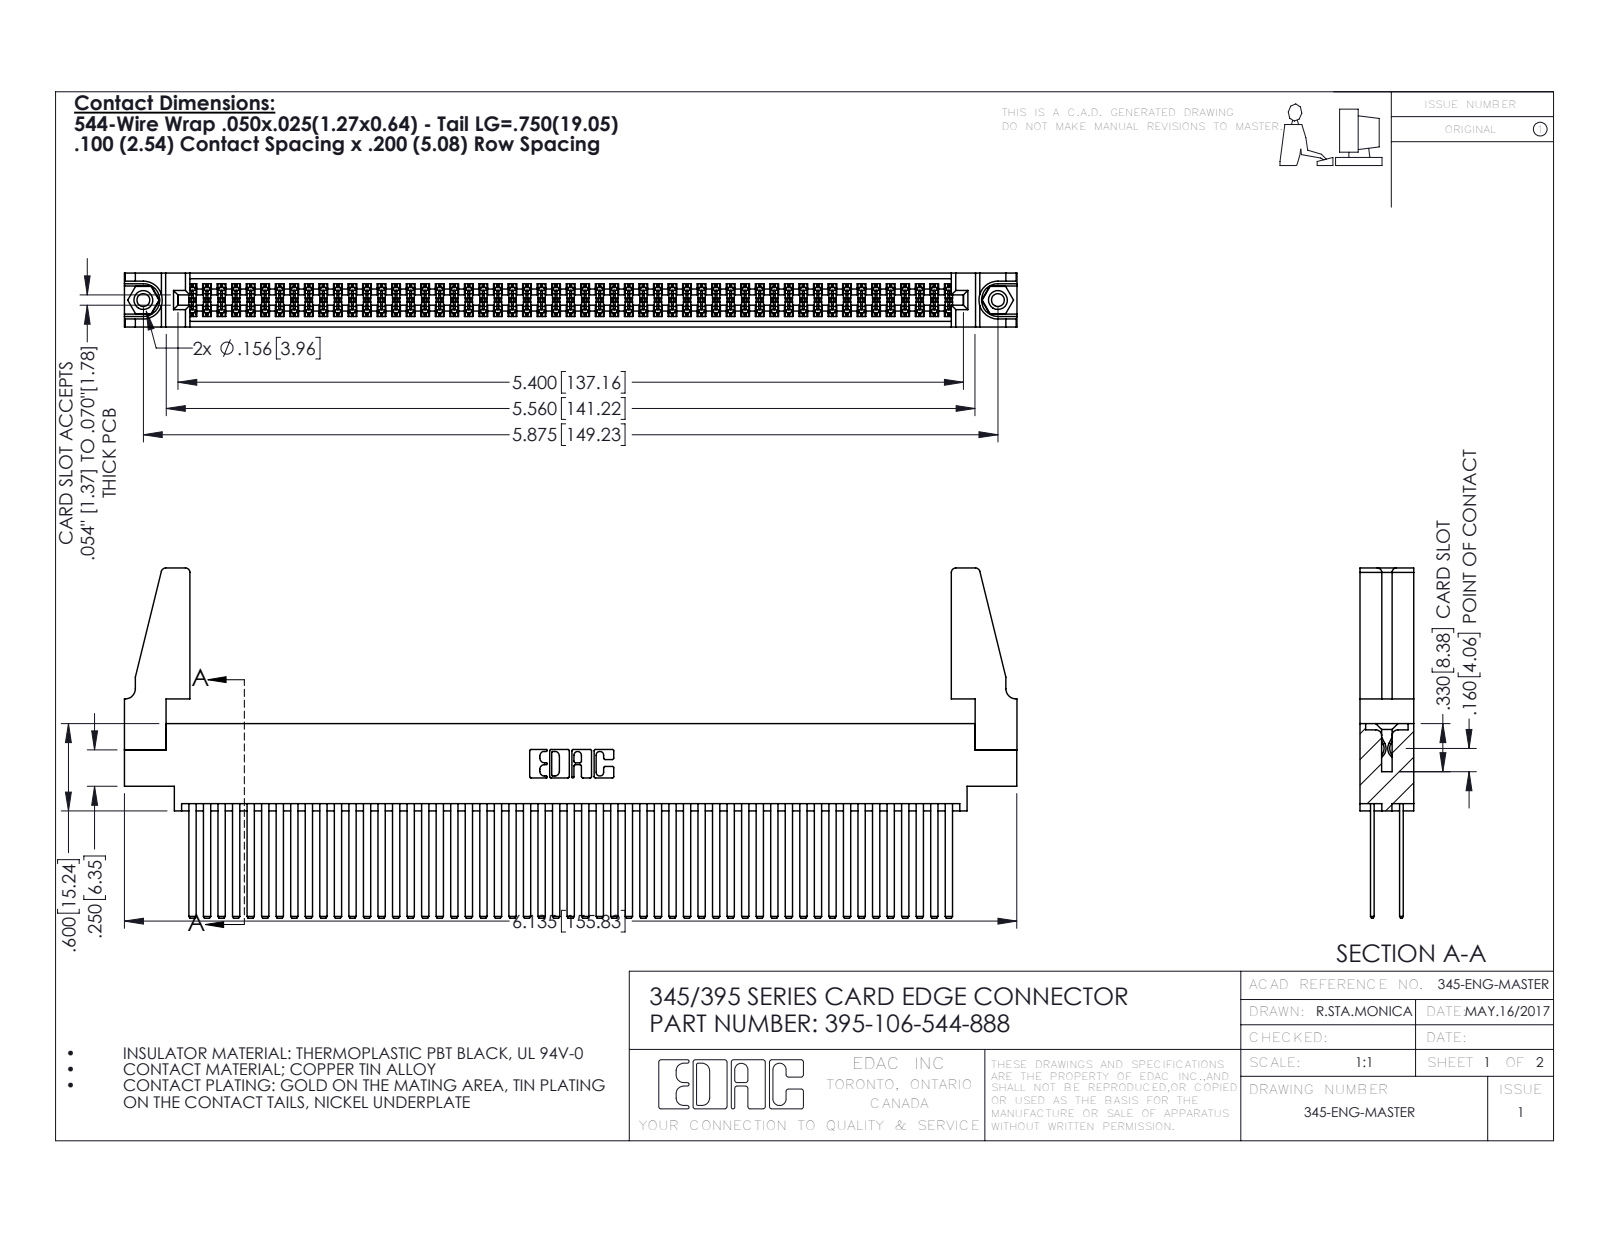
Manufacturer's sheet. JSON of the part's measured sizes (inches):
{"part_name": "345-220-078_345-220-088; 345 Part_0.170 Offset - 0.156 Dia-TH; 395-106-544-888; 345-292-001_345-293-144 (+1 more)", "step_written_by": "SolidWorks 2016 (CONFIG_CONTROL_DESIGN)", "units": "inches", "bodies": {"solids": 111, "faces": 4918, "planar": 3230, "cylindrical": 1672, "other": 16}, "overall_size": [6.136, 2.407, 0.37], "volume_in3": 1.212, "surface_area_in2": 50.21, "round_holes": [[0.089, 2], [0.125, 2], [0.156, 2], [0.064, 1]], "round_bosses_or_shafts": [[0.155, 2]], "partial_cylinders_radius": [[0.006, 159], [0.01, 22], [0.03, 8], [0.007, 6], [0.031, 6], [0.026, 3], [0.014, 2], [0.019, 2]], "face_to_face_distances": [0.072, 0.298, 0.2, 0.098, 0.272, 0.025, 0.225, 0.37, 0.175, 0.149], "hole_center_spacings": [0.27, 5.639, 5.875]}
